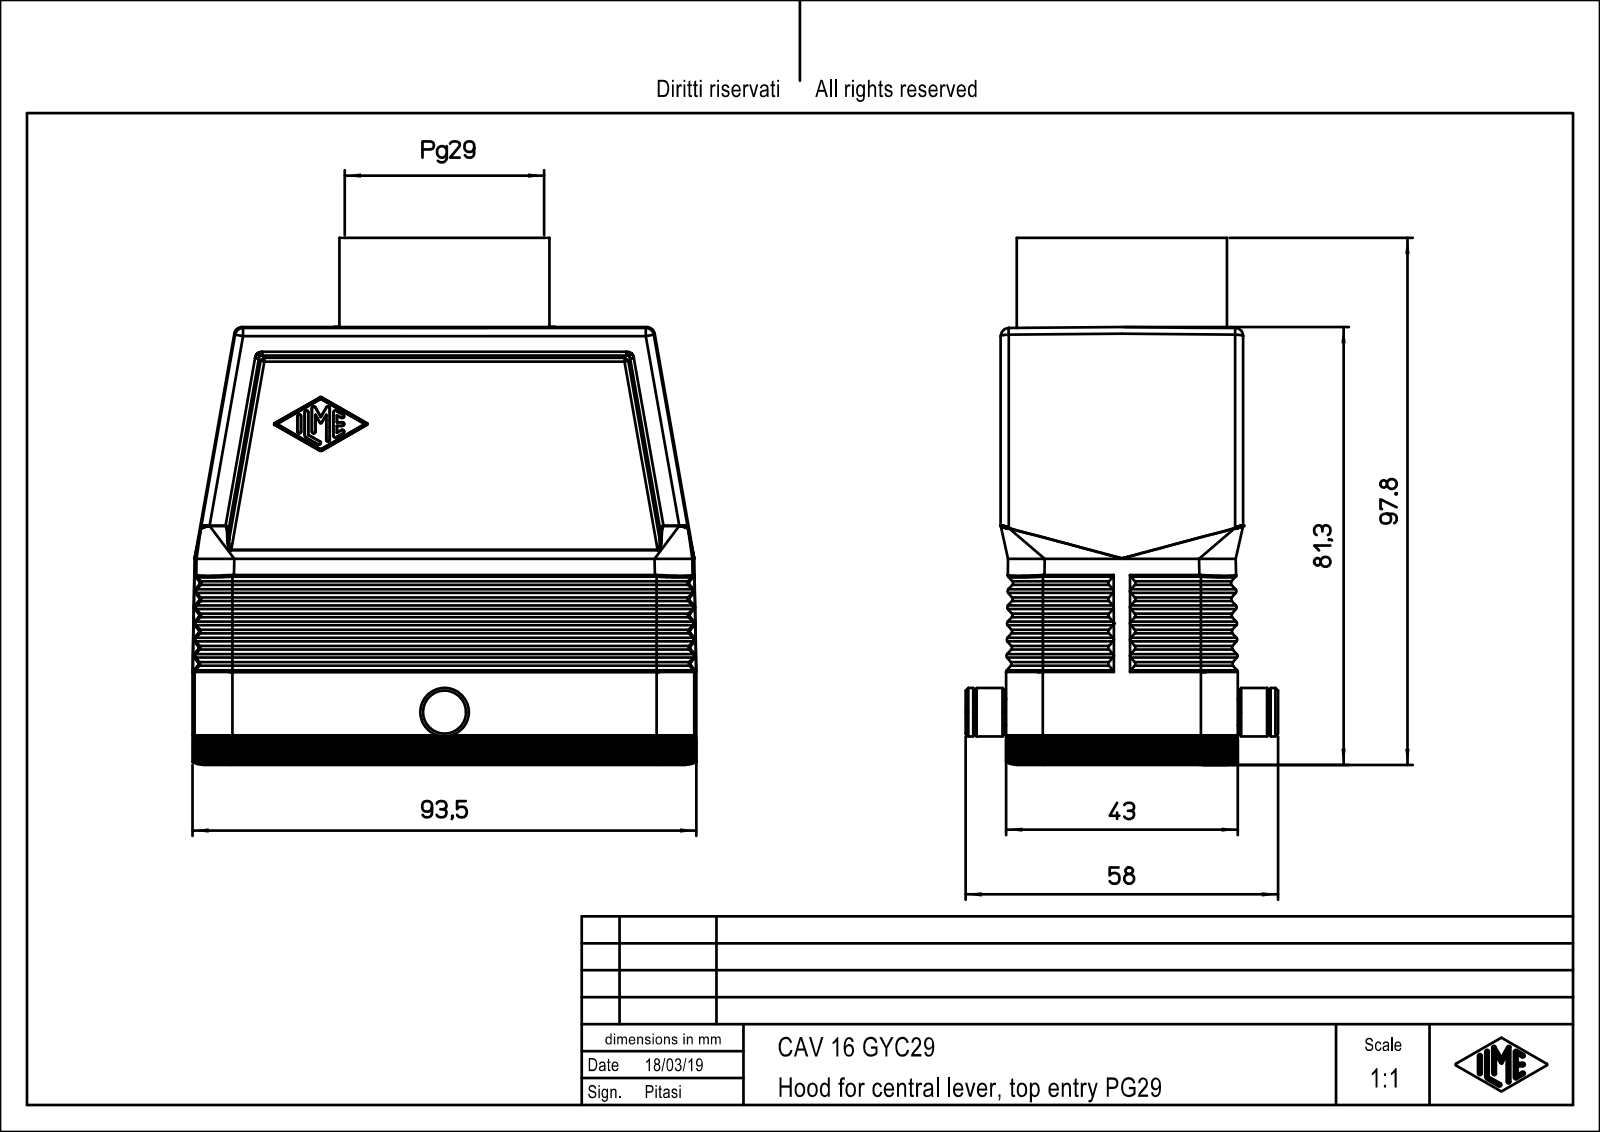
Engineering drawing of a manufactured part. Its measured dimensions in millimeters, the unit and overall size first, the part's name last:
Units: millimetres
Overall size (bounding box): 97.75 × 93.5 × 58
Round holes (diameter × count): ⌀32 ×1, ⌀36.24 ×1
Round bosses / shafts (diameter × count): ⌀39 ×1, ⌀37 ×1, ⌀9 ×1, ⌀4.8 ×1
Partial cylindrical surfaces — rounded edges, fillets, slot ends (radius × count): R0.5 ×84, R1 ×16, R7 ×12, R1.5 ×10, R3 ×8, R3.5 ×4, R4 ×4, R4.2 ×4
Main face-to-face distances: 43, 4, 1.01, 2, 6, 7, 44, 1, 39, 5
Volume: 106 008 mm³ · Surface area: 51 717 mm²
Bodies: 1 solid, 599 faces (231 planar, 186 cylindrical, 182 other)
Part name (STEP PRODUCT): CAV_16_GYC29
STEP written by: PTC Creo Elements/Direct Modeling 19.0E 27-Jun-2016 (C) Parametric Technology GmbH (AUTOMOTIVE_DESIGN)
